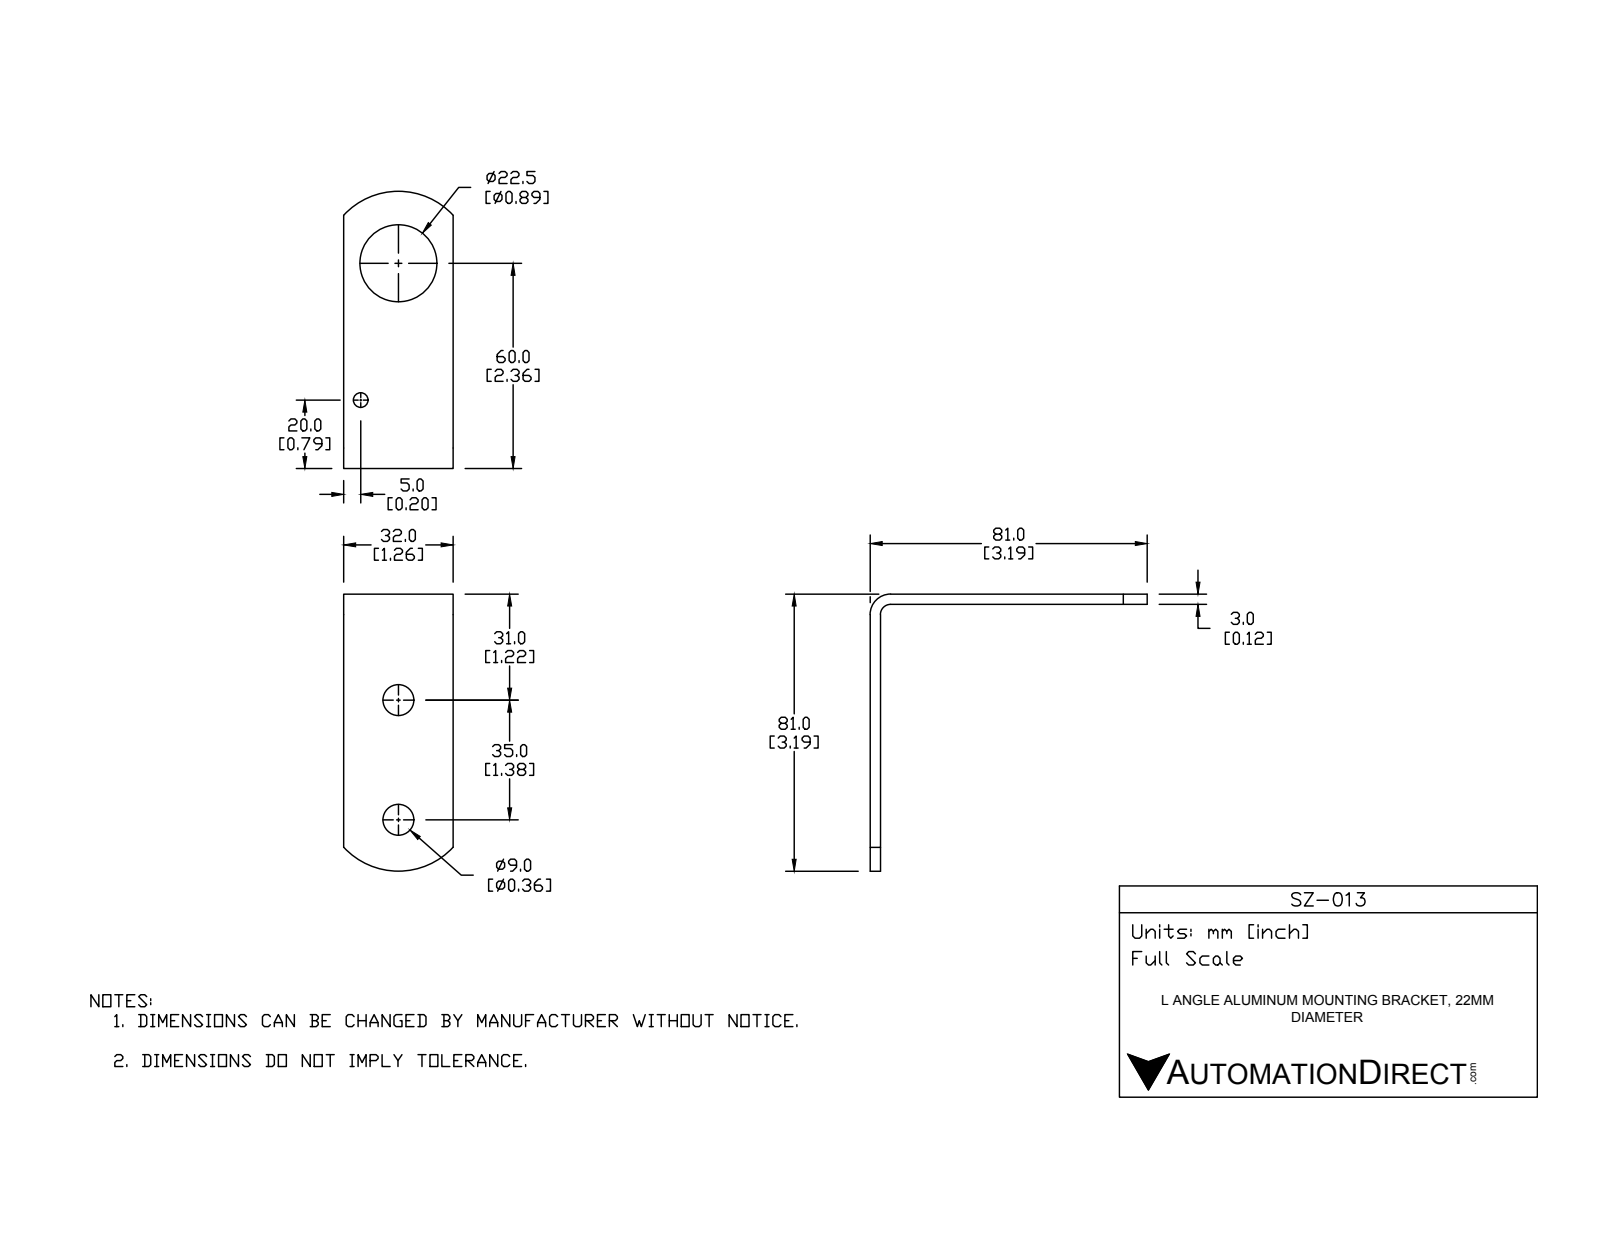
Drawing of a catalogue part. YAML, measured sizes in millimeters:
part_name: "SZ-013"
step_written_by: "SolidWorks 2016 (AUTOMOTIVE_DESIGN)"
units: millimeters
bodies: {solids: 1, faces: 22, planar: 10, cylindrical: 12, other: 0}
overall_size: [81, 81, 32]
volume: 13043
surface_area: 10192
round_holes:
  - {diameter: 9.04, count: 2}
  - {diameter: 4.3, count: 1}
  - {diameter: 22.5, count: 1}
partial_cylinders:
  - {radius: 21.79, count: 2}
  - {radius: 3, count: 1}
  - {radius: 6, count: 1}
face_to_face_distances: [3, 32]
hole_center_spacings: [35, 41.48]
